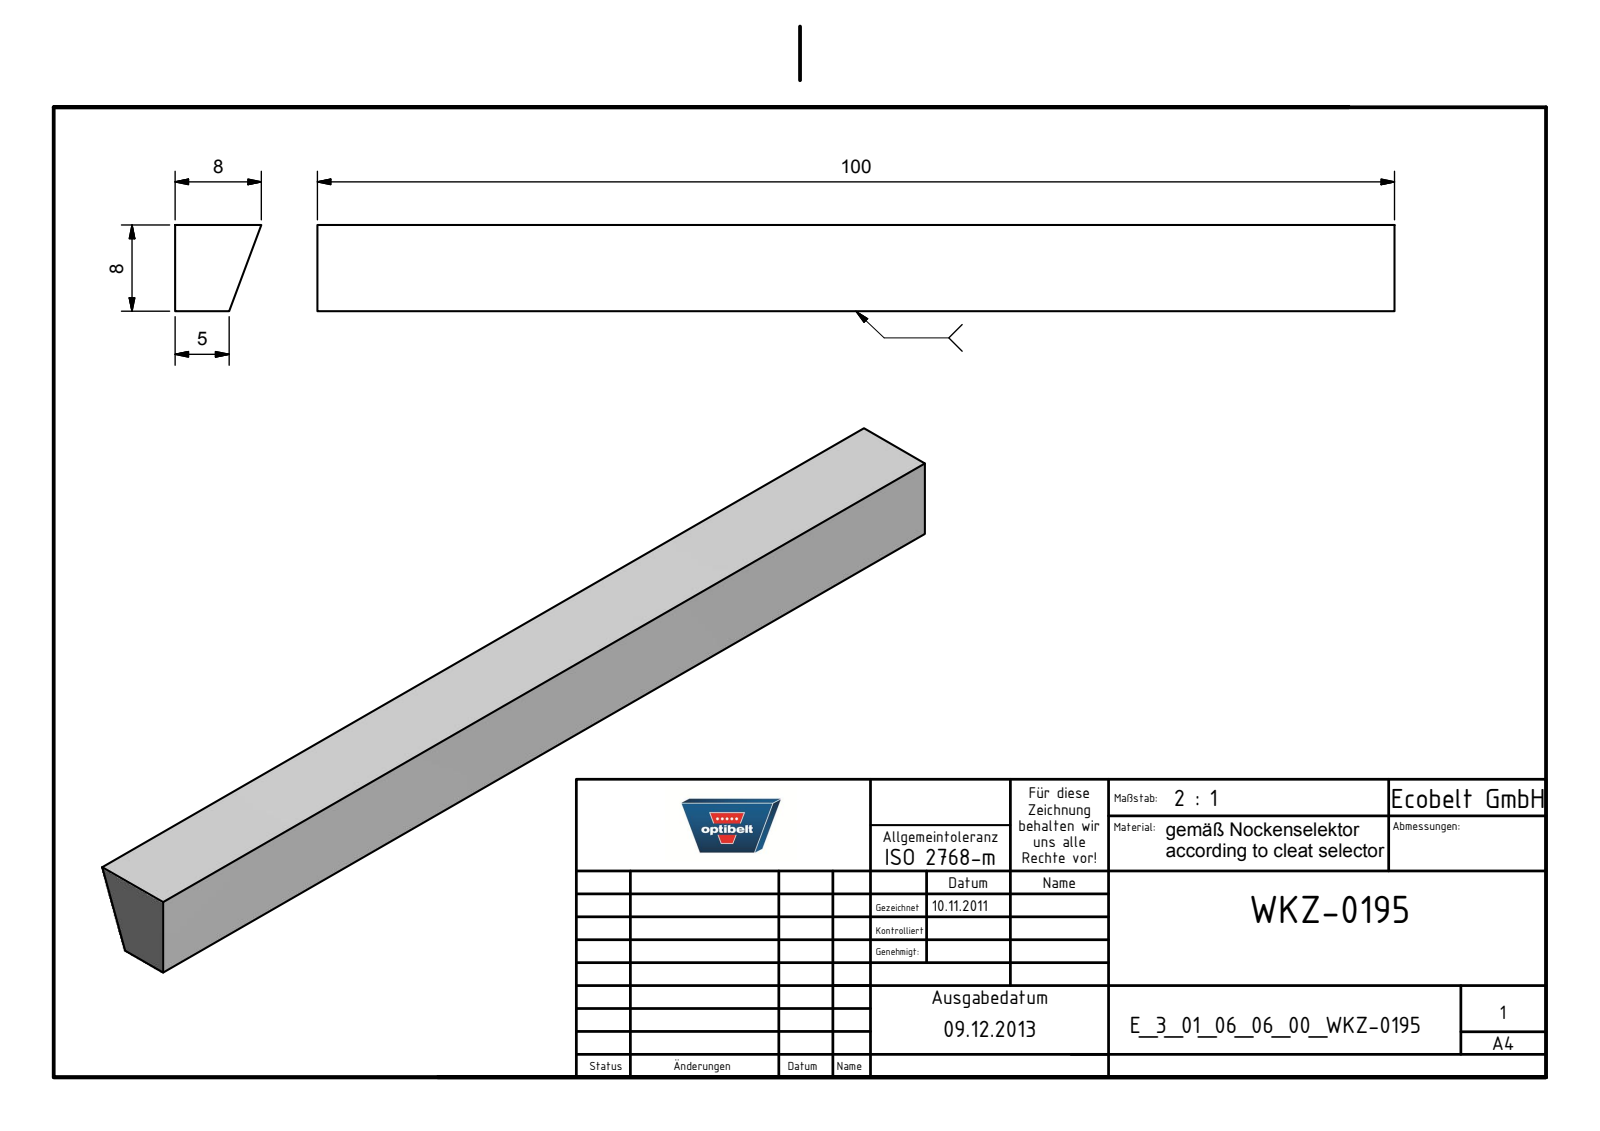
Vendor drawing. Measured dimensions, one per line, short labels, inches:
name: E_3_01_06_06_00_WKZ-0195
written by: Autodesk Inventor 2025 (AUTOMOTIVE_DESIGN)
unit: in
bodies: 1 solid, 6 faces (6 planar, 0 cylindrical, 0 other)
size: 3.937 × 0.315 × 0.315
volume: 0.317 in³; area: 4.74 in²
face distances: 0.315, 3.937
